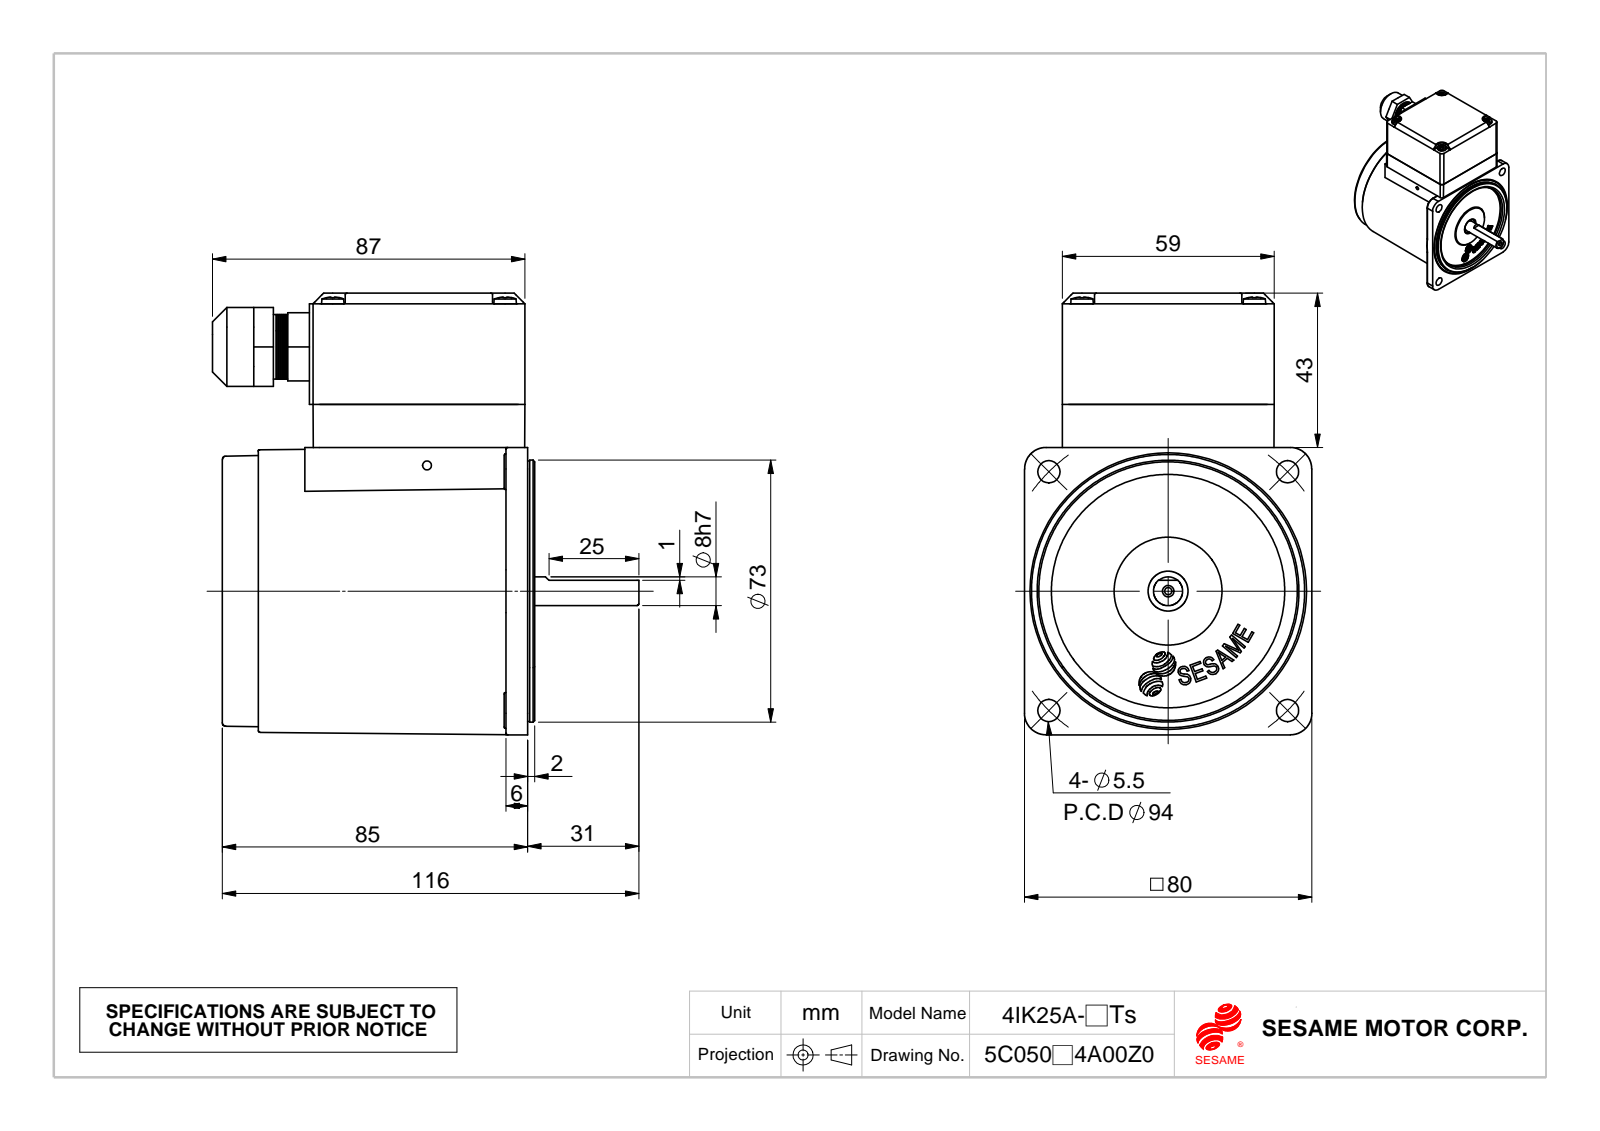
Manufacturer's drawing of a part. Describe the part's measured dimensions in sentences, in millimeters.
The part is named "成品180度; Ts下墊片; M425TsA_成品; C475-C473_C475成品-車工 (+1 more)". Its 3-D file was written by "SolidWorks 2010 (CONFIG_CONTROL_DESIGN)". It is 11 solids with 2628 faces: 271 planar, 929 cylindrical and 1428 other. Overall it measures 123 by 118.75 by 80 millimeters. Its volume is 255 365 cubic millimeters and its surface area 101 015 square millimeters. Round holes: 4 of diameter 3.3, 4 of diameter 3.5, 4 of diameter 3.9, 4 of diameter 4.3, 4 of diameter 6.2, 2 of diameter 11, 1 of diameter 2, 1 of diameter 2.5, 1 of diameter 12, 1 of diameter 14.5, 1 of diameter 60, 1 of diameter 65. Round bosses or shafts: 4 of diameter 6.3, 4 of diameter 3, 1 of diameter 72.93, 1 of diameter 72.53, 1 of diameter 37, 1 of diameter 22, 1 of diameter 18, 1 of diameter 8. Partial cylindrical surfaces (rounded edges, fillets, slot ends): 12 of radius 0.5, 12 of radius 2, 8 of radius 0.61, 8 of radius 1.16, 8 of radius 1.29, 8 of radius 2.26, 6 of radius 4, 4 of radius 0.16. The main face-to-face distances are 12, 1, 1.5, 0.5, 3, 0.75, 84, 80, 83, 82.5. The hole center spacings are 46.99, 48, 66.46, 11.67, 12.35, 12.7, 24.93, 25.
